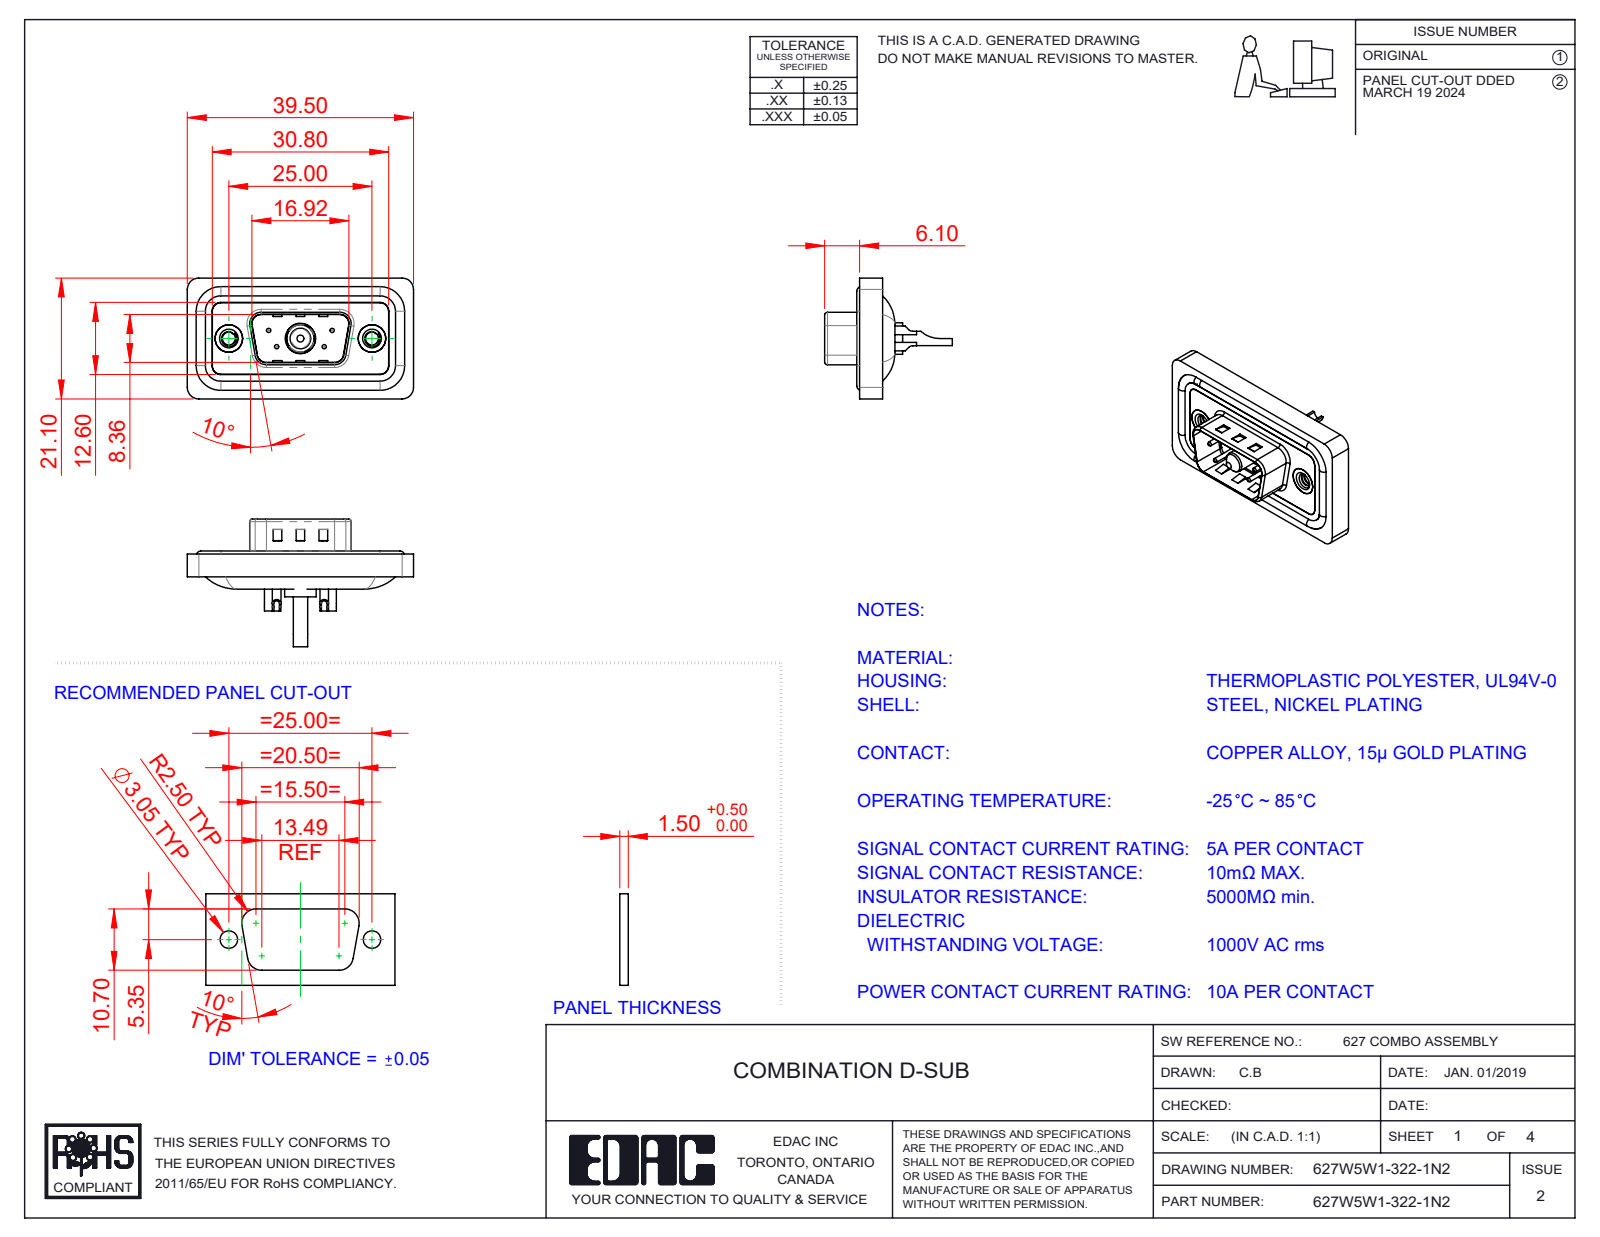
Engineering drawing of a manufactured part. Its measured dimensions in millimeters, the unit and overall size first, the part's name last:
Units: millimetres
Overall size (bounding box): 39.5 × 22.3 × 21.1
Round holes (diameter × count): ⌀0.75 ×4, ⌀1 ×4, ⌀1.6 ×4, ⌀2 ×4, ⌀2.26 ×2, ⌀4 ×2, ⌀4.8 ×2, ⌀5 ×2, ⌀1.7 ×1, ⌀4.85 ×1, ⌀5.3 ×1
Round bosses / shafts (diameter × count): ⌀1.6 ×4, ⌀1.5 ×4, ⌀4.9 ×2, ⌀5.5 ×1, ⌀5.2 ×1, ⌀4.75 ×1, ⌀3.75 ×1, ⌀3.6 ×1
Partial cylindrical surfaces — rounded edges, fillets, slot ends (radius × count): R1.5 ×22, R2 ×18, R0.5 ×8, R1.6 ×8, R1 ×6, R0.25 ×4, R0.6 ×4, R0.65 ×4
Main face-to-face distances: 0.4, 1.1, 2.9, 1.6, 1.5, 3.1, 0.5, 2.5, 4, 0.8
Hole centre spacings: 3.16, 5.72, 7.1, 12.5, 18.1, 4.39, 4.4, 8.31
Volume: 4 391 mm³ · Surface area: 7 021 mm²
Bodies: 13 solids, 604 faces (193 planar, 266 cylindrical, 145 other)
Part name (STEP PRODUCT): 627Combo Shell Rear_09 Contacts; 627Combo Shell Front_09 Contacts; 627Combo Contact Row 2_22; 627Combo Waterproof Housing_09 Contacts (+5 more)
STEP written by: SolidWorks 2023 (CONFIG_CONTROL_DESIGN)
